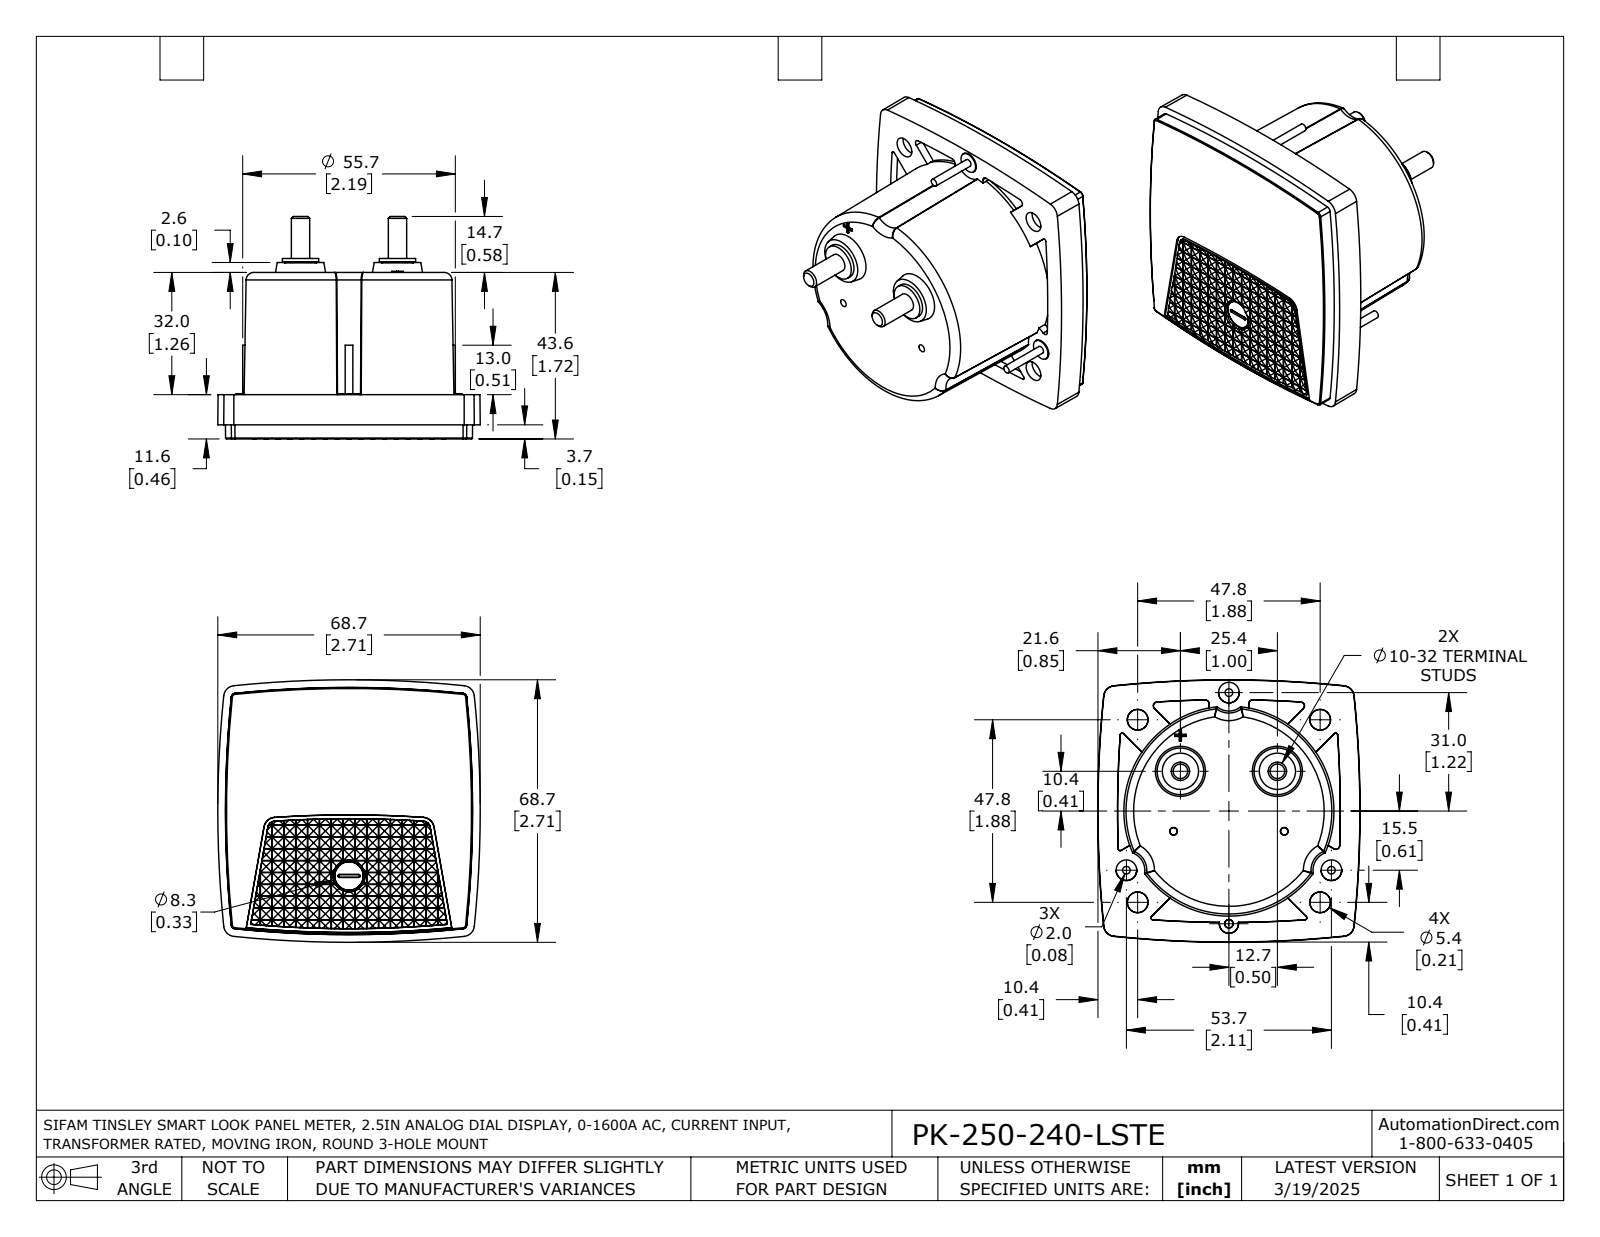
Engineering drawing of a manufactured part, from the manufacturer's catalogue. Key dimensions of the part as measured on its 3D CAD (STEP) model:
Part name (STEP PRODUCT): PK-250-240-LSTE
STEP written by: SolidWorks 2021 (AUTOMOTIVE_DESIGN)
Units: inches
Bodies: 1 solid, 1550 faces (1165 planar, 265 cylindrical, 120 other)
Overall size (bounding box): 2.706 × 2.706 × 2.297
Volume: 7.594 in³ · Surface area: 30.41 in²
Round bosses / shafts (diameter × count): ⌀0.213 ×3, ⌀0.079 ×3, ⌀0.374 ×2, ⌀0.189 ×2, ⌀0.215 ×1
Partial cylindrical surfaces — rounded edges, fillets, slot ends (radius × count): R0.167 ×2, R1.083 ×1
Main face-to-face distances: 1.717, 1.26, 0.457, 0.024, 0.087, 0.096, 0.311, 0.12, 0.072, 1.346
